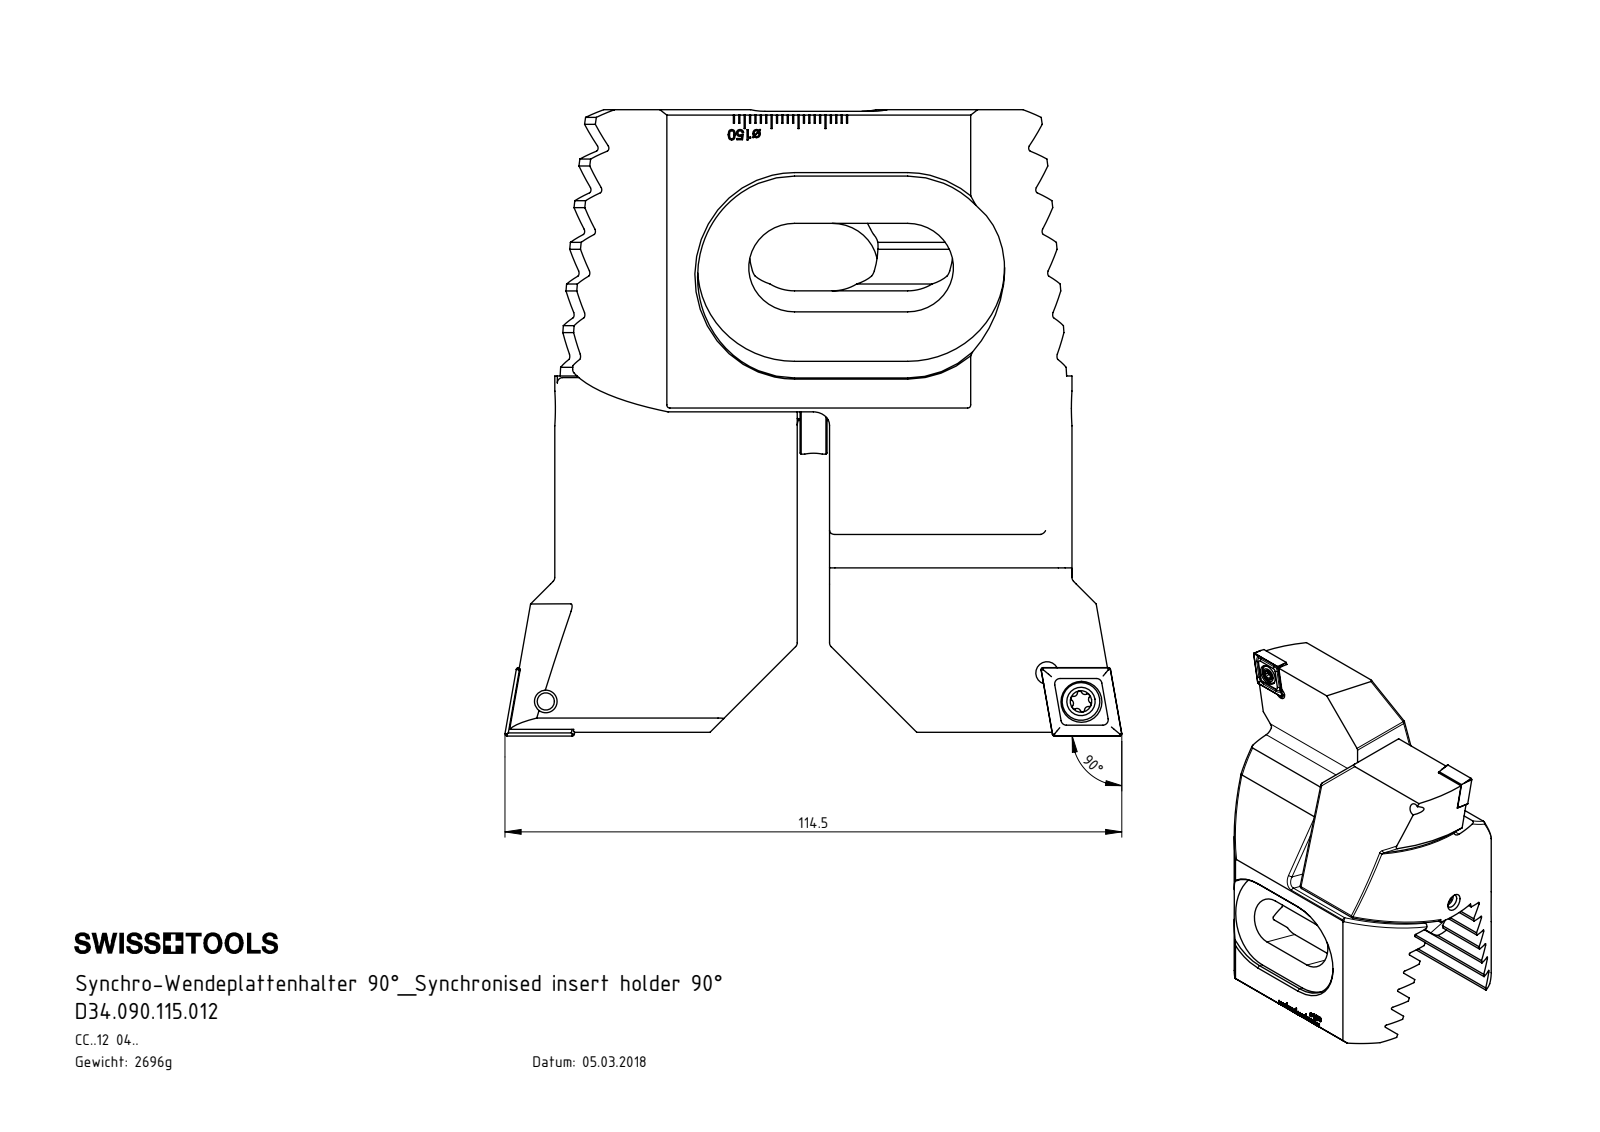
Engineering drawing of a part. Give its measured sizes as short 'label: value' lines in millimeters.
name: Z94-xxx.001.067_E; CCMT120404; WCC-ER2.001.010_A; Z94-ER3.001.090_A (+4 more)
written by: SolidWorks 2017 (CONFIG_CONTROL_DESIGN)
unit: mm
bodies: 11 solids, 853 faces (469 planar, 154 cylindrical, 230 other)
size: 115.5 × 114.5 × 75.2
volume: 343 499 mm³; area: 65 522 mm²
holes: 4× ⌀4.2, 3× ⌀3.3, 2× ⌀2, 2× ⌀5.5, 2× ⌀7.6, 1× ⌀5
bosses: 3× ⌀4, 2× ⌀7, 2× ⌀5, 1× ⌀17, 1× ⌀6, 1× ⌀3.8
rounds: 16× R1, 12× R0.39, 12× R0.58, 8× R0.69, 6× R3, 4× R0.69, 4× R8.5, 4× R12
face distances: 6.93, 20.78, 27.71, 13.85, 13.86, 13.19, 37.3, 37.9, 6.92, 1.59
hole spacings: 8.21, 8.33, 25, 93.2, 93.29, 99.43, 48.3, 86.76
